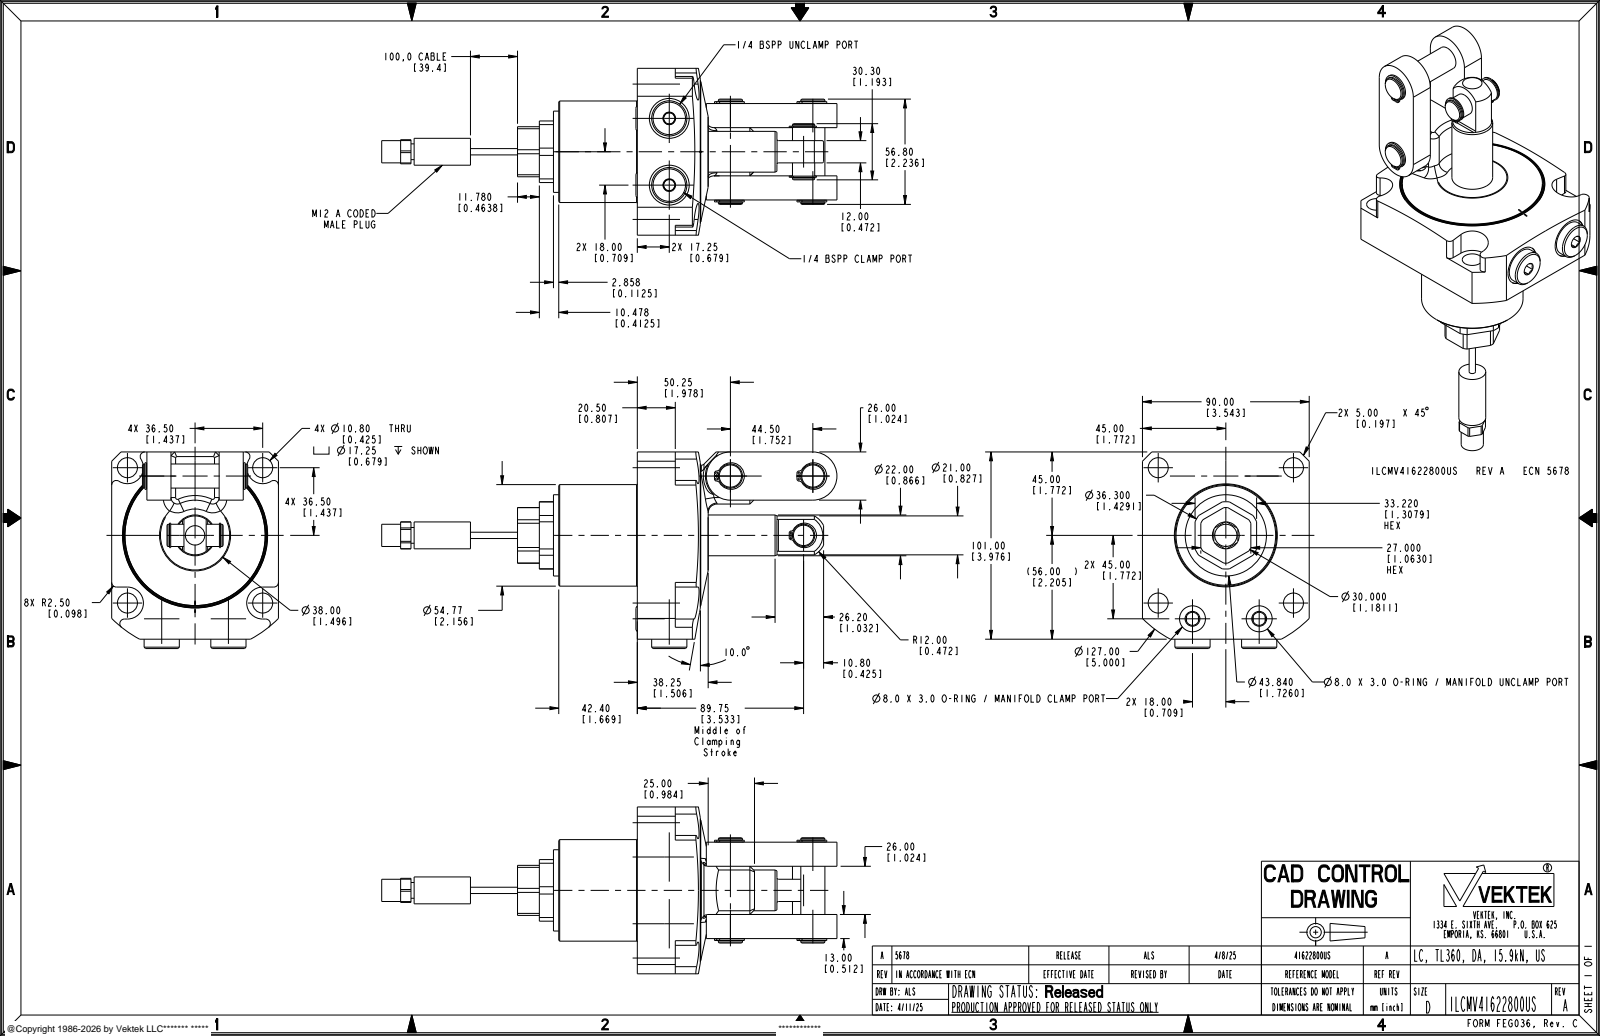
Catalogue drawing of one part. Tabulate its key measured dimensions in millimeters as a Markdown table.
| quantity | value |
| --- | --- |
| part name | ILCMV41622800_BODY_US; ILCMV41622800_LUG_US; ILCMV41622800US |
| STEP written by | CREO PARAMETRIC BY PTC INC, 2021164 (AUTOMOTIVE_DESIGN) |
| units | millimeters |
| bodies | 4 solids, 457 faces (168 planar, 197 cylindrical, 92 other) |
| overall size | 245.71 × 106.06 × 90 |
| volume | 501 305 mm³ |
| surface area | 83 491 mm² |
| round holes (diameter × count) | 1.19 × 4, 10.8 × 4, 1.04 × 2, 7.04 × 2, 11.89 × 2, 14 × 2, 21.5 × 2, 75.79 × 1 |
| round bosses / shafts (diameter × count) | 19 × 2, 14.33 × 2, 13.16 × 2, 13 × 2, 11.89 × 2, 11.2 × 2, 8 × 2, 75.68 × 1 |
| partial cylindrical surfaces (radius × count) | 2.5 × 8, 0.8 × 4, 1.19 × 4, 1.82 × 4, 8.62 × 4, 1.04 × 2, 1.35 × 2, 3.5 × 2 |
| main face-to-face distances | 21.25, 19, 71, 32, 39, 90, 13, 26, 58, 52 |
| hole center spacings | 51.62, 73, 3.1, 20.36, 36, 44.5, 44.61, 48.47 |
